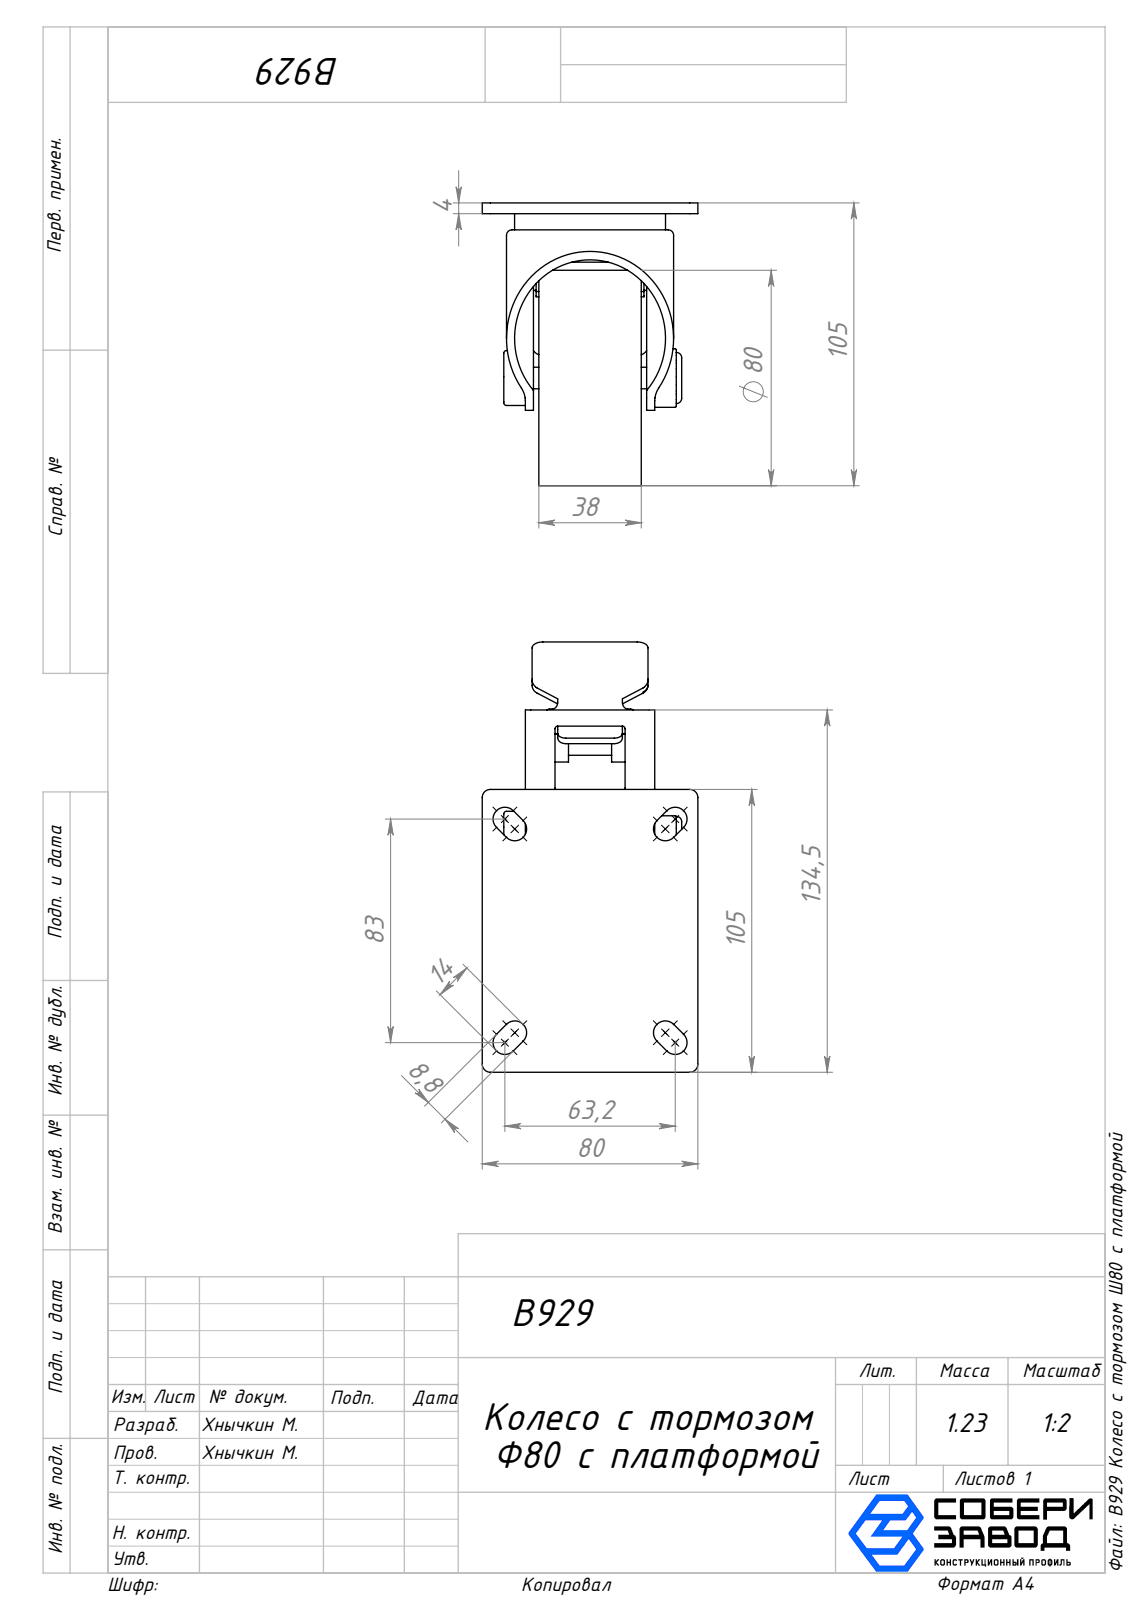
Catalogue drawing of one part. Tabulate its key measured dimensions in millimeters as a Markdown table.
| quantity | value |
| --- | --- |
| part name | B929 Вал_00; B929 Крепление для лепестка_00; B929 Закрытая гайка_00; B929 Вал Ф3 для тормоза_00 (+6 more) |
| STEP written by | SolidWorks 2025 (AUTOMOTIVE_DESIGN) |
| units | millimeters |
| bodies | 9 solids, 338 faces (126 planar, 159 cylindrical, 53 other) |
| overall size | 160.83 × 105 × 80 |
| volume | 246 853 mm³ |
| surface area | 91 225 mm² |
| round holes (diameter × count) | 3 × 2, 8 × 2, 62 × 2, 50 × 1 |
| round bosses / shafts (diameter × count) | 40 × 2, 80 × 1, 62 × 1, 56 × 1, 6 × 1 |
| partial cylindrical surfaces (radius × count) | 1 × 35, 0.5 × 12, 2 × 12, 3 × 10, 4.4 × 8, 5 × 6, 1.5 × 2, 4 × 2 |
| main face-to-face distances | 3, 4, 5, 2, 6, 43.01, 40.01, 13, 45.01, 10 |
| hole center spacings | 46.39 |
